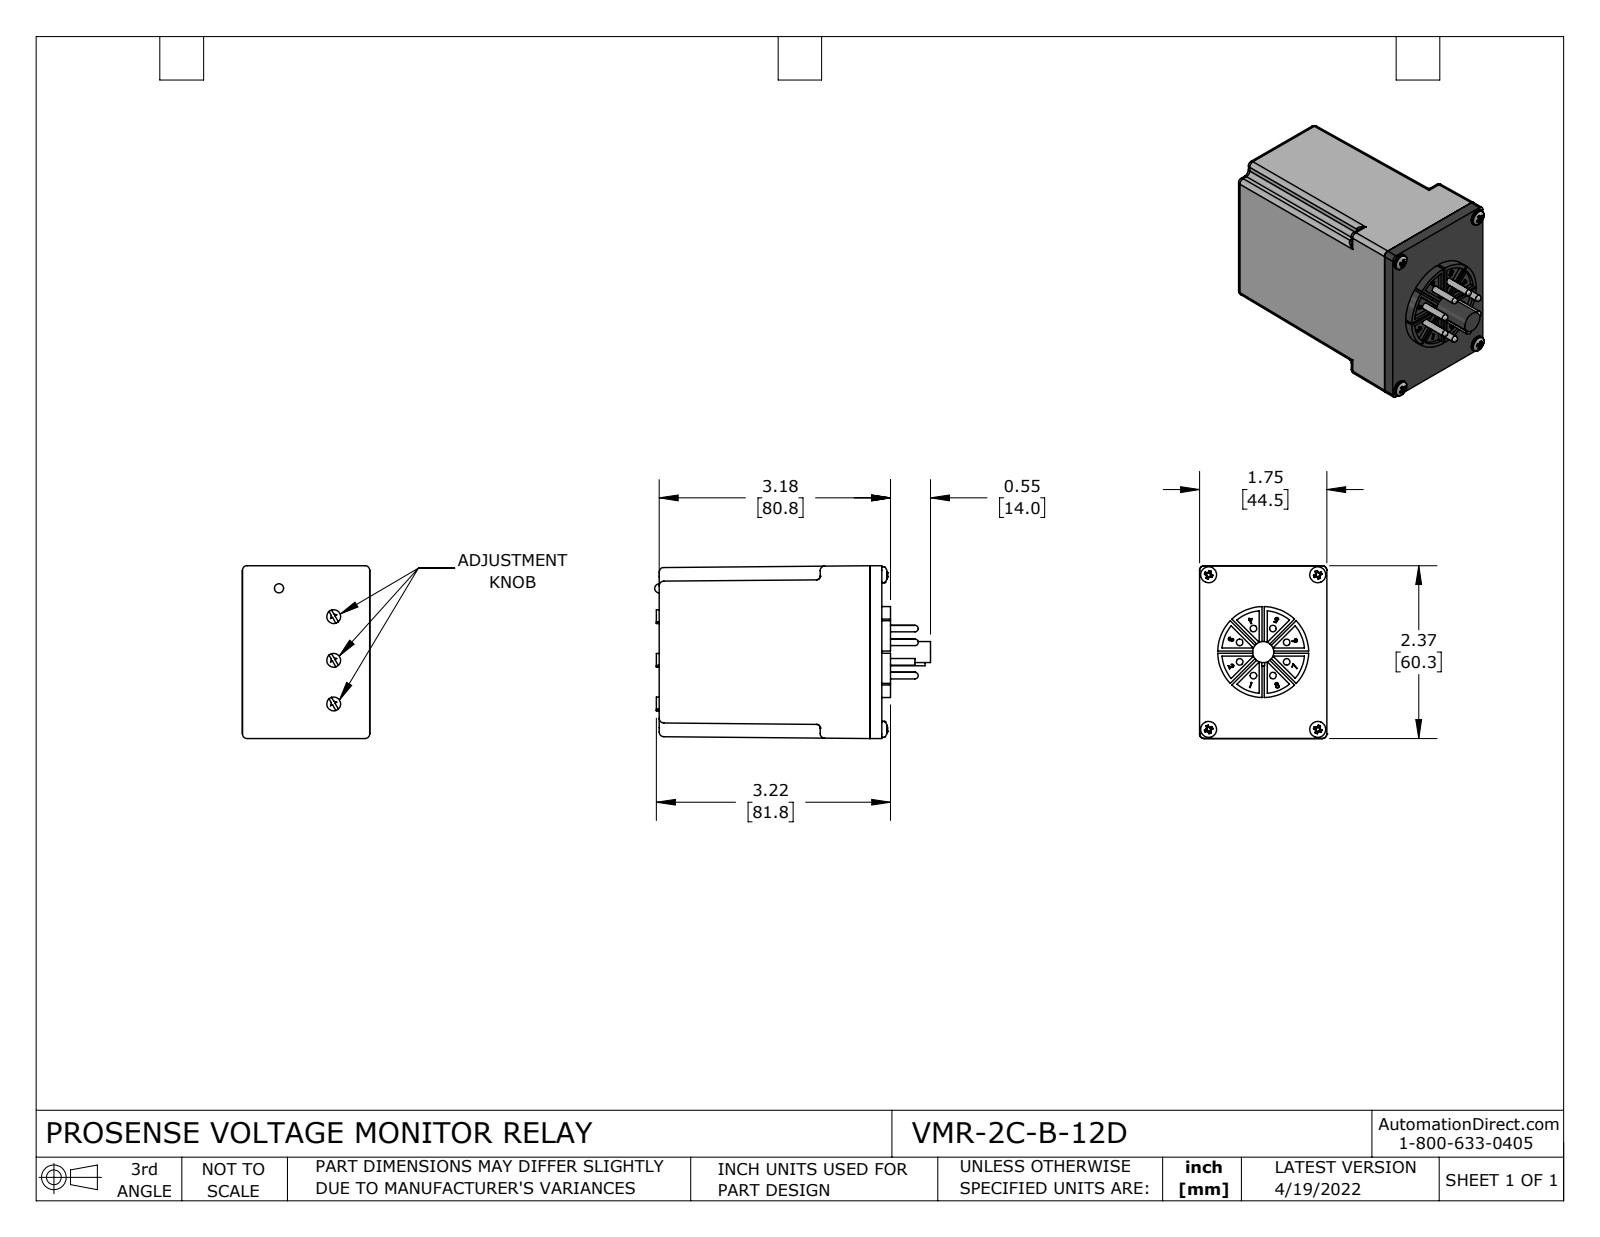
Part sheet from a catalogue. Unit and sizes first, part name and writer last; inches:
Units: inches
Overall size (bounding box): 3.79 × 2.375 × 1.75
Round holes (diameter × count): ⌀0.125 ×4
Round bosses / shafts (diameter × count): ⌀0.09 ×8, ⌀0.219 ×4, ⌀0.19 ×3, ⌀1.25 ×1, ⌀0.29 ×1
Partial cylindrical surfaces — rounded edges, fillets, slot ends (radius × count): R0.063 ×32, R0.005 ×8, R0.05 ×4, R0.57 ×1
Main face-to-face distances: 2.9, 0.16, 3.06, 0.07, 0.23, 3.13, 0.188, 0.05, 0.12, 0.28
Hole centre spacings: 1.5, 2.125, 2.601
Volume: 12.25 in³ · Surface area: 44.71 in²
Bodies: 18 solids, 574 faces (249 planar, 170 cylindrical, 155 other)
Part name (STEP PRODUCT): VMR-2C-B-12D
STEP written by: SolidWorks 2021 (CONFIG_CONTROL_DESIGN)
